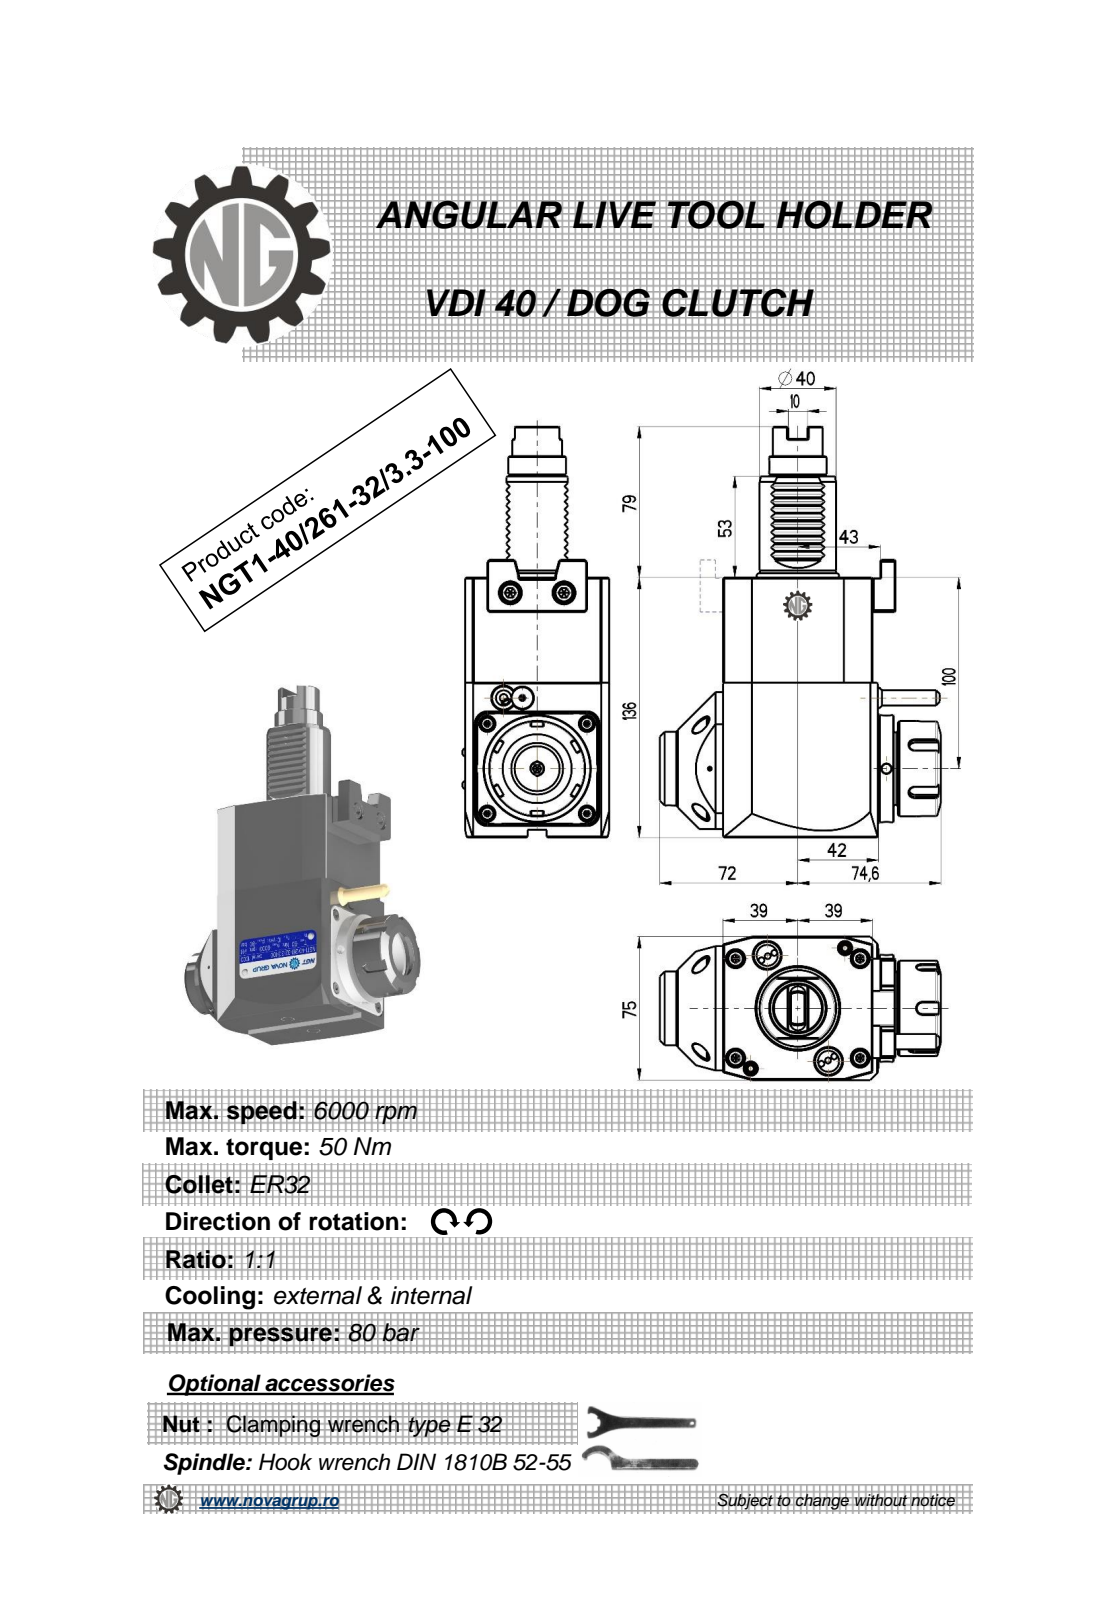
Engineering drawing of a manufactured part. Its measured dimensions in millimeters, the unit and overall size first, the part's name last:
Units: millimetres
Overall size (bounding box): 215 × 146.6 × 75
Round holes (diameter × count): ⌀5 ×3, ⌀3 ×1, ⌀4.2 ×1, ⌀27 ×1
Round bosses / shafts (diameter × count): ⌀56 ×1, ⌀50 ×1, ⌀43 ×1, ⌀40 ×1, ⌀38.5 ×1, ⌀30 ×1, ⌀26 ×1, ⌀11.2 ×1
Partial cylindrical surfaces — rounded edges, fillets, slot ends (radius × count): R0.3 ×20, R0.22 ×6, R3 ×5, R0.5 ×2, R1 ×2, R12.5 ×1, R40 ×1
Main face-to-face distances: 75, 136, 78, 81, 3, 0.5, 84.88, 1, 80.8, 2.8
Hole centre spacings: 40.93, 122.75, 158.5
Volume: 1 027 000 mm³ · Surface area: 79 146 mm²
Bodies: 1 solid, 427 faces (227 planar, 79 cylindrical, 121 other)
Part name (STEP PRODUCT): NGT1_40_261_32_3_3_100
STEP written by: PRO/ENGINEER BY PARAMETRIC TECHNOLOGY CORPORATION, 2010280 (CONFIG_CONTROL_DESIGN)
